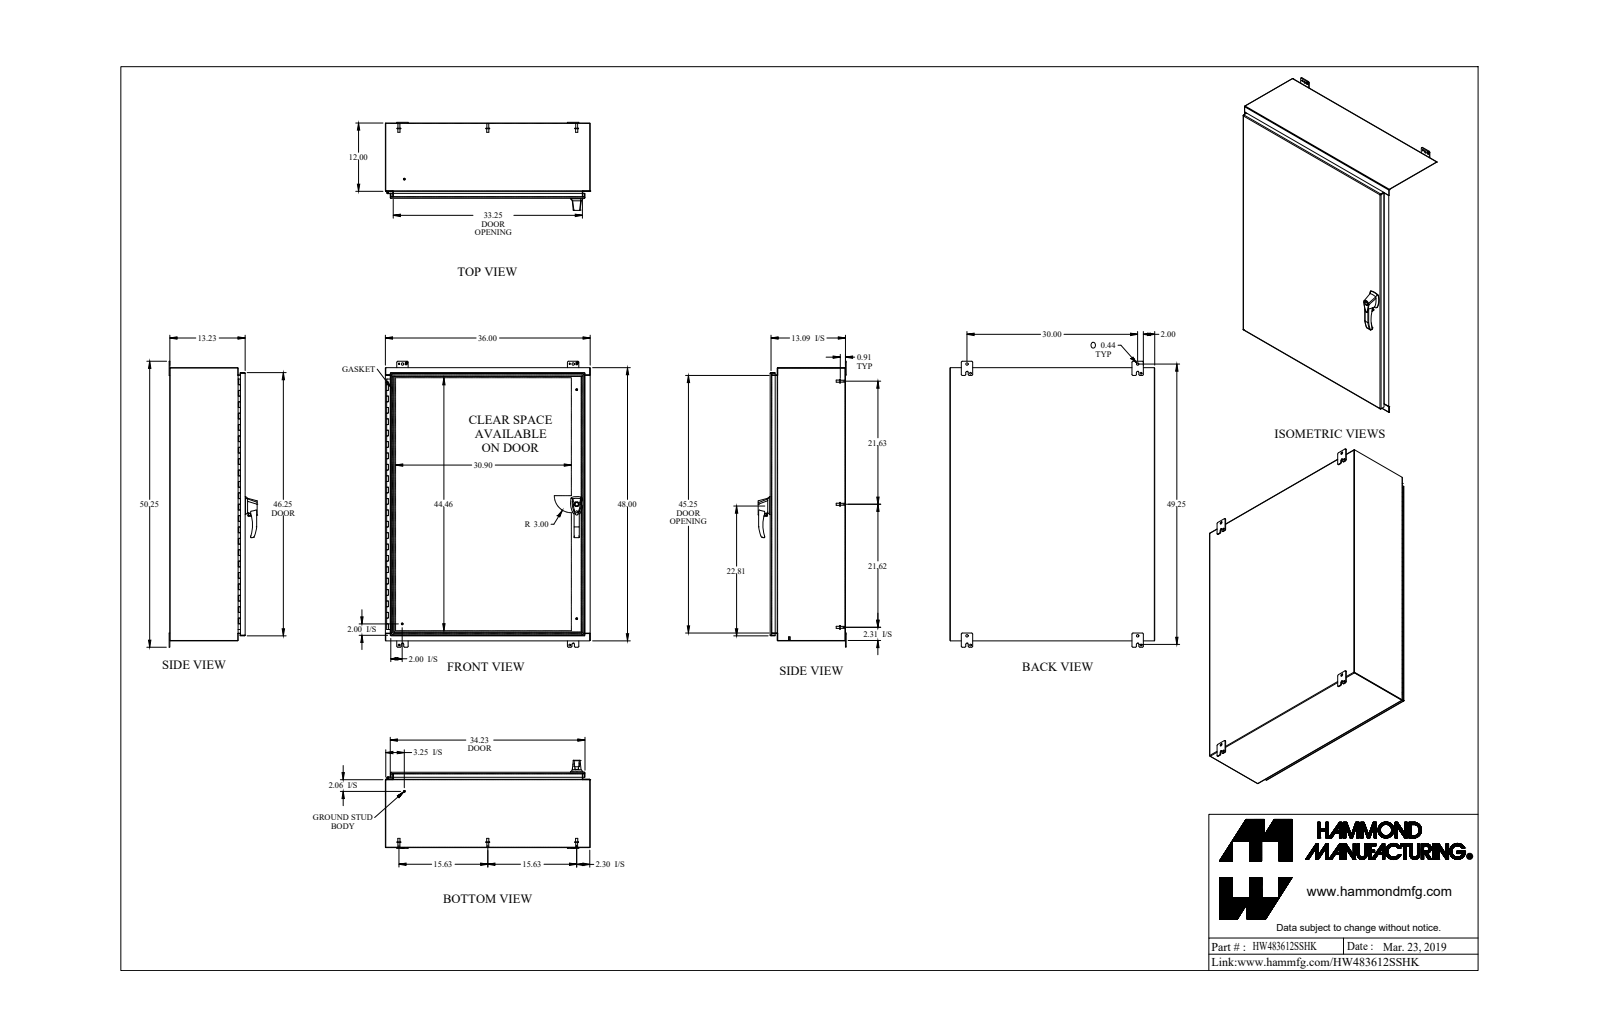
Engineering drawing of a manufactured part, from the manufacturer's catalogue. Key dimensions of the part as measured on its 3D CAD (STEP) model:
Part name (STEP PRODUCT): HW483612SSHK
STEP written by: SolidWorks 2018 (AUTOMOTIVE_DESIGN)
Units: inches
Bodies: 48 solids, 1592 faces (761 planar, 693 cylindrical, 138 other)
Overall size (bounding box): 50.25 × 36 × 15.473
Volume: 508.2 in³ · Surface area: 12 596 in²
Round holes (diameter × count): ⌀0.176 ×6, ⌀0.313 ×5, ⌀0.25 ×3, ⌀0.265 ×3, ⌀0.413 ×3, ⌀0.196 ×2, ⌀0.256 ×2, ⌀0.394 ×2, ⌀0.437 ×2, ⌀0.187 ×1, ⌀0.233 ×1, ⌀0.33 ×1
Round bosses / shafts (diameter × count): ⌀0.375 ×13, ⌀0.65 ×8, ⌀0.332 ×8, ⌀0.25 ×7, ⌀0.156 ×6, ⌀1 ×3, ⌀0.51 ×3, ⌀0.63 ×2
Partial cylindrical surfaces — rounded edges, fillets, slot ends (radius × count): R0.25 ×27, R0.188 ×20, R0.036 ×14, R0.108 ×14, R0.06 ×12, R0.125 ×9, R0.218 ×8, R0.03 ×6
Main face-to-face distances: 0.072, 13.138, 13.066, 0.095, 13.233, 13.161, 35.928, 47.928, 35.856, 36
Hole centre spacings: 1.111, 20.118, 20.119, 40.237, 20.119, 30, 30.665, 38.744
